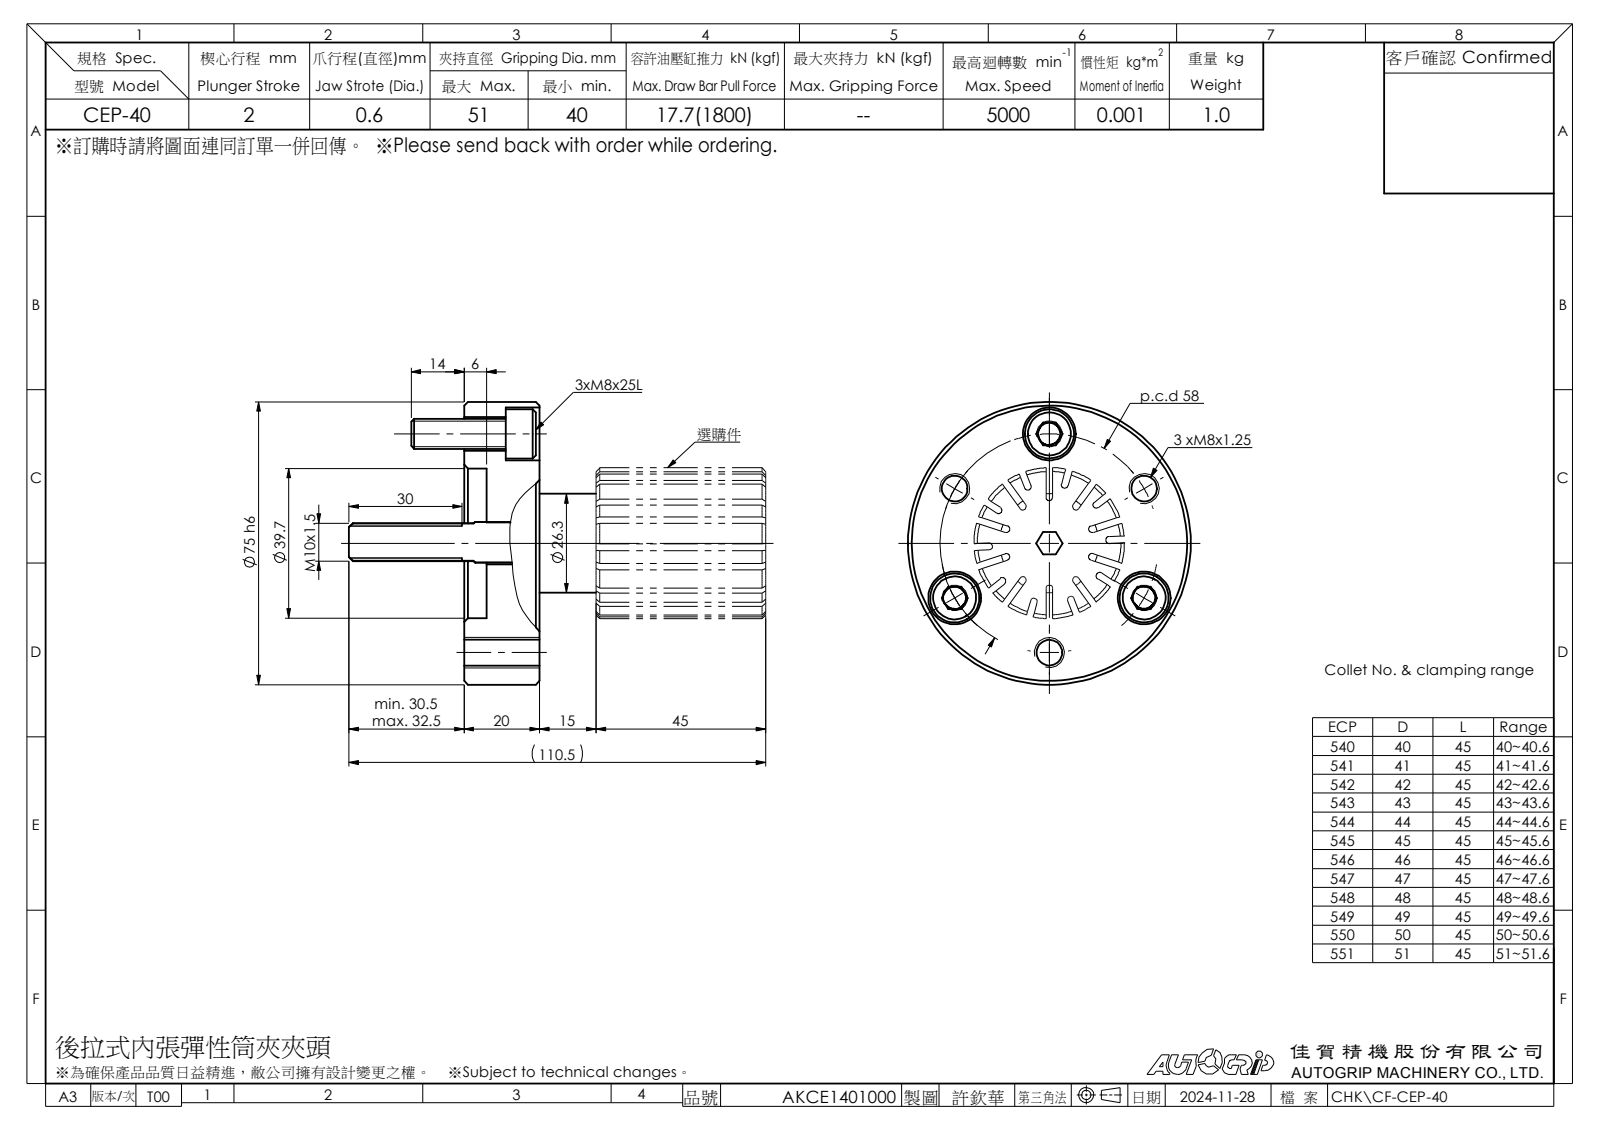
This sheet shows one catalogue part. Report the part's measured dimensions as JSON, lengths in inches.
{"part_name": "CF-CEP-40; 圓頭內六角螺栓_M8x25; CF-CEP-40-02000; CF-CEP-40-01000", "step_written_by": "SolidWorks 2020 (CONFIG_CONTROL_DESIGN)", "units": "inches", "bodies": {"solids": 5, "faces": 237, "planar": 122, "cylindrical": 61, "other": 54}, "overall_size": [4.35, 2.953, 2.953], "volume_in3": 8.096, "surface_area_in2": 67.58, "round_holes": [[0.268, 3], [0.354, 3], [0.551, 3], [0.437, 1], [1.563, 1]], "round_bosses_or_shafts": [[0.512, 3], [0.315, 3], [2.953, 1], [1.035, 1], [0.425, 1], [0.394, 1]], "partial_cylinders_radius": [[0.035, 20], [0.787, 1]], "face_to_face_distances": [0.071, 0.787, 0.236, 0.551, 3.15, 2.913, 2.362, 1.142, 0.197, 2.717], "hole_center_spacings": [1.142, 1.978, 1.977, 2.283, 2.283]}
